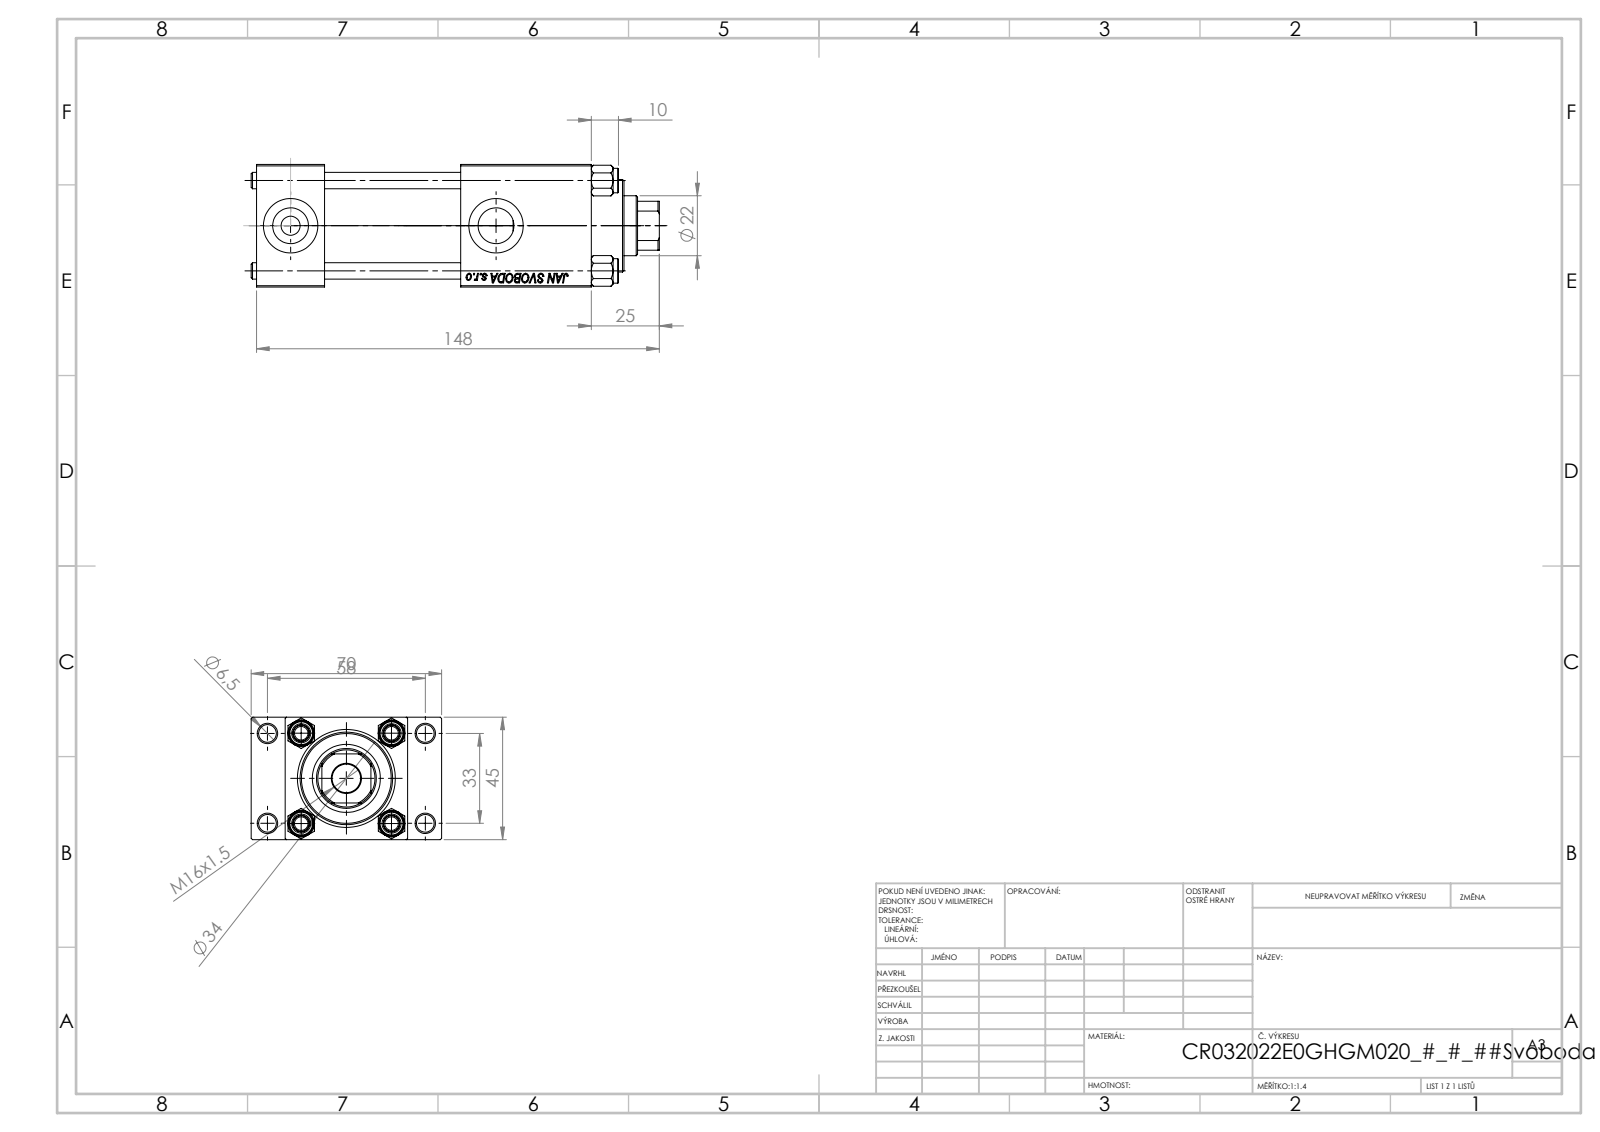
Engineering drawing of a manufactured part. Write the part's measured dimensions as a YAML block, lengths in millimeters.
part_name: "V215_VC_A; V215CR_E_Body; V215CR_TYCINKA_E; NUT_M5_E (+1 more)"
step_written_by: "SolidWorks 2019 (CONFIG_CONTROL_DESIGN)"
units: millimeters
bodies: {solids: 11, faces: 1135, planar: 497, cylindrical: 86, other: 552}
overall_size: [150, 70, 45]
volume: 236088
surface_area: 80866
round_holes:
  - {diameter: 6, count: 4}
  - {diameter: 6.5, count: 4}
  - {diameter: 7, count: 2}
  - {diameter: 13.16, count: 2}
  - {diameter: 20, count: 2}
  - {diameter: 10.5, count: 1}
  - {diameter: 22, count: 1}
  - {diameter: 24, count: 1}
  - {diameter: 25, count: 1}
  - {diameter: 32, count: 1}
  - {diameter: 33, count: 1}
round_bosses_or_shafts:
  - {diameter: 9, count: 4}
  - {diameter: 38, count: 1}
  - {diameter: 34, count: 1}
partial_cylinders:
  - {radius: 10.5, count: 1}
face_to_face_distances: [45, 25, 12.5, 57.5, 123, 50, 75, 98, 48, 94.3]
hole_center_spacings: [12.4, 23.48, 33.2, 33.37, 35.35, 45.6, 56.35, 33]
